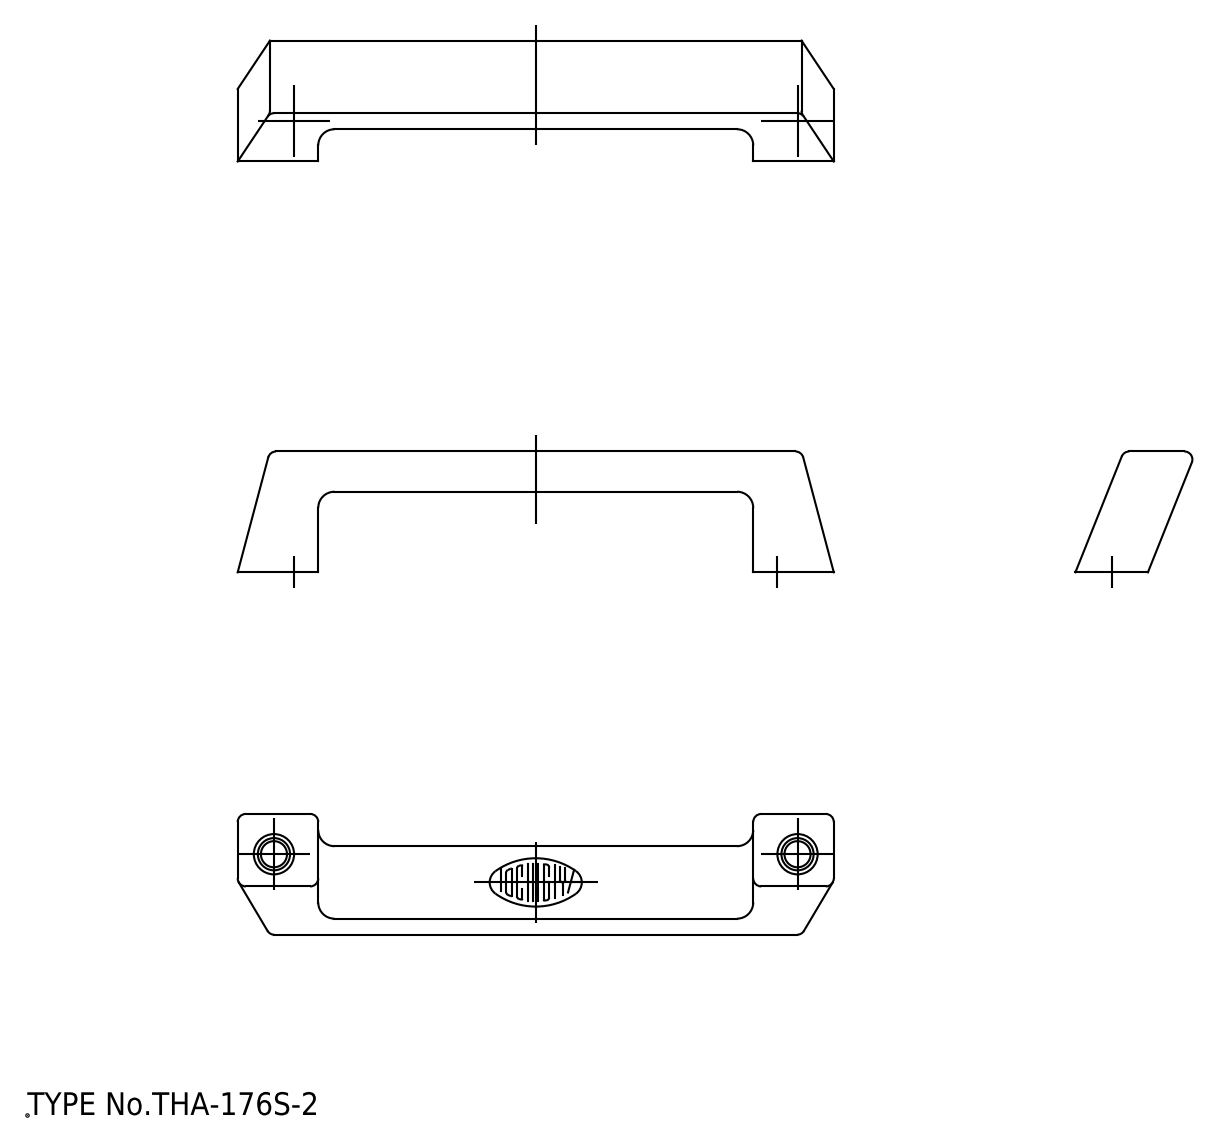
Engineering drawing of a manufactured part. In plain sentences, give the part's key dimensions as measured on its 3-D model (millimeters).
Its 3-D file was written by "spGate 19.8.4 (****-****-****-****) (AUTOMOTIVE_DESIGN)". It is 1 solid with 40 faces: 12 planar, 20 cylindrical and 8 other. Overall it measures 74 by 15 by 14.52 millimeters. Its volume is 4 138 cubic millimeters and its surface area 2 703 square millimeters. Round holes: 2 of diameter 4. Partial cylindrical surfaces (rounded edges, fillets, slot ends): 14 of radius 1, 2 of radius 2. The main face-to-face distances are 8.35, 15, 54, 5, 10. The hole center spacings are 65.
